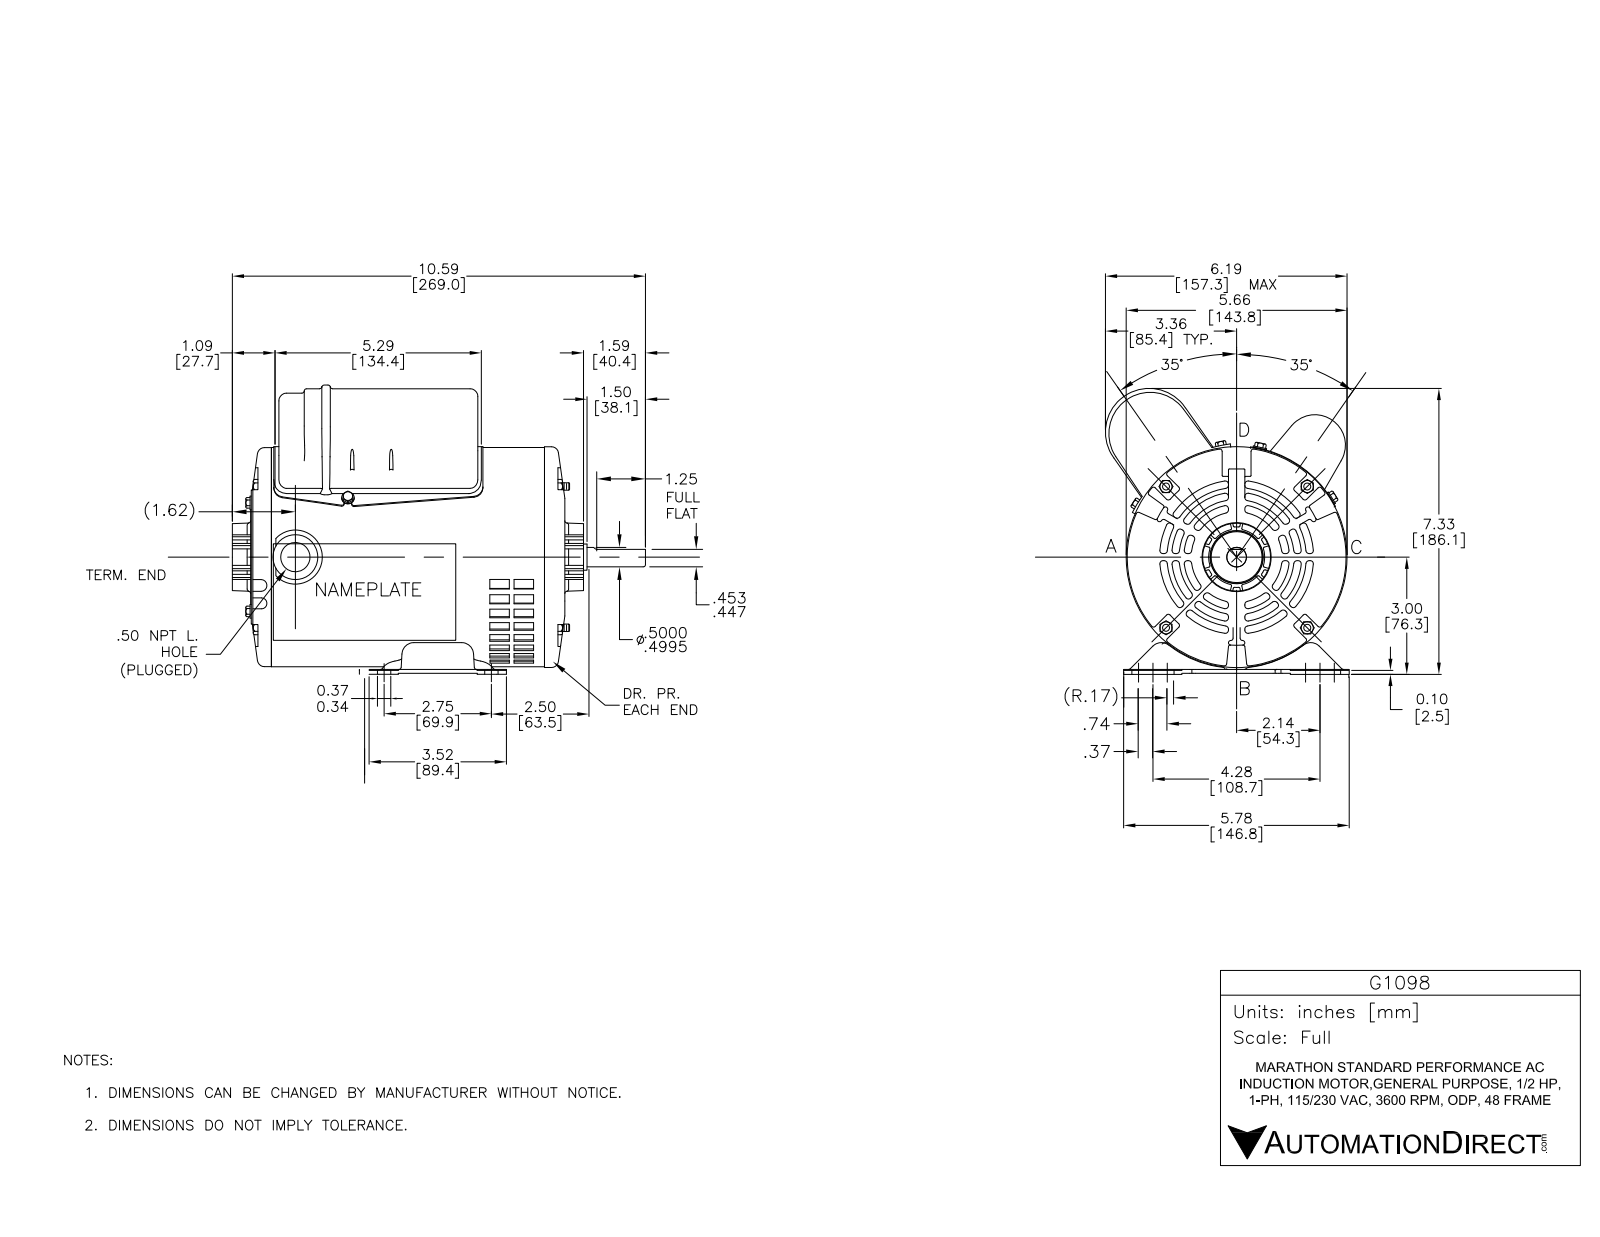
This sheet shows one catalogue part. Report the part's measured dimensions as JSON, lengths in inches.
{"part_name": "G1098A SS404113-700_RevB B3", "step_written_by": "SolidWorks 2017 (AUTOMOTIVE_DESIGN)", "units": "inches", "bodies": {"solids": 29, "faces": 4076, "planar": 1318, "cylindrical": 770, "other": 1988}, "overall_size": [10.59, 7.066, 6.049], "volume_in3": 27.88, "surface_area_in2": 689.8, "round_holes": [[0.153, 11], [0.38, 6], [0.25, 5], [0.193, 4], [0.22, 4], [0.218, 2], [0.457, 1], [0.505, 1], [0.64, 1], [0.669, 1], [0.687, 1], [0.73, 1]], "round_bosses_or_shafts": [[0.164, 6], [0.399, 4], [0.348, 4], [0.19, 4], [0.166, 4], [0.335, 2], [5.62, 1], [5.615, 1]], "partial_cylinders_radius": [[0.06, 52], [0.03, 44], [0.015, 32], [0.02, 27], [0.25, 25], [0.01, 24], [0.05, 20], [0.12, 19]], "face_to_face_distances": [0.026, 7.66, 0.105, 5.116, 7.531, 0.531, 0.104, 7.7, 0.041, 0.08], "hole_center_spacings": [2.562, 3.624, 1.12, 1.19, 2.4, 2.578, 4.243, 4.82]}
